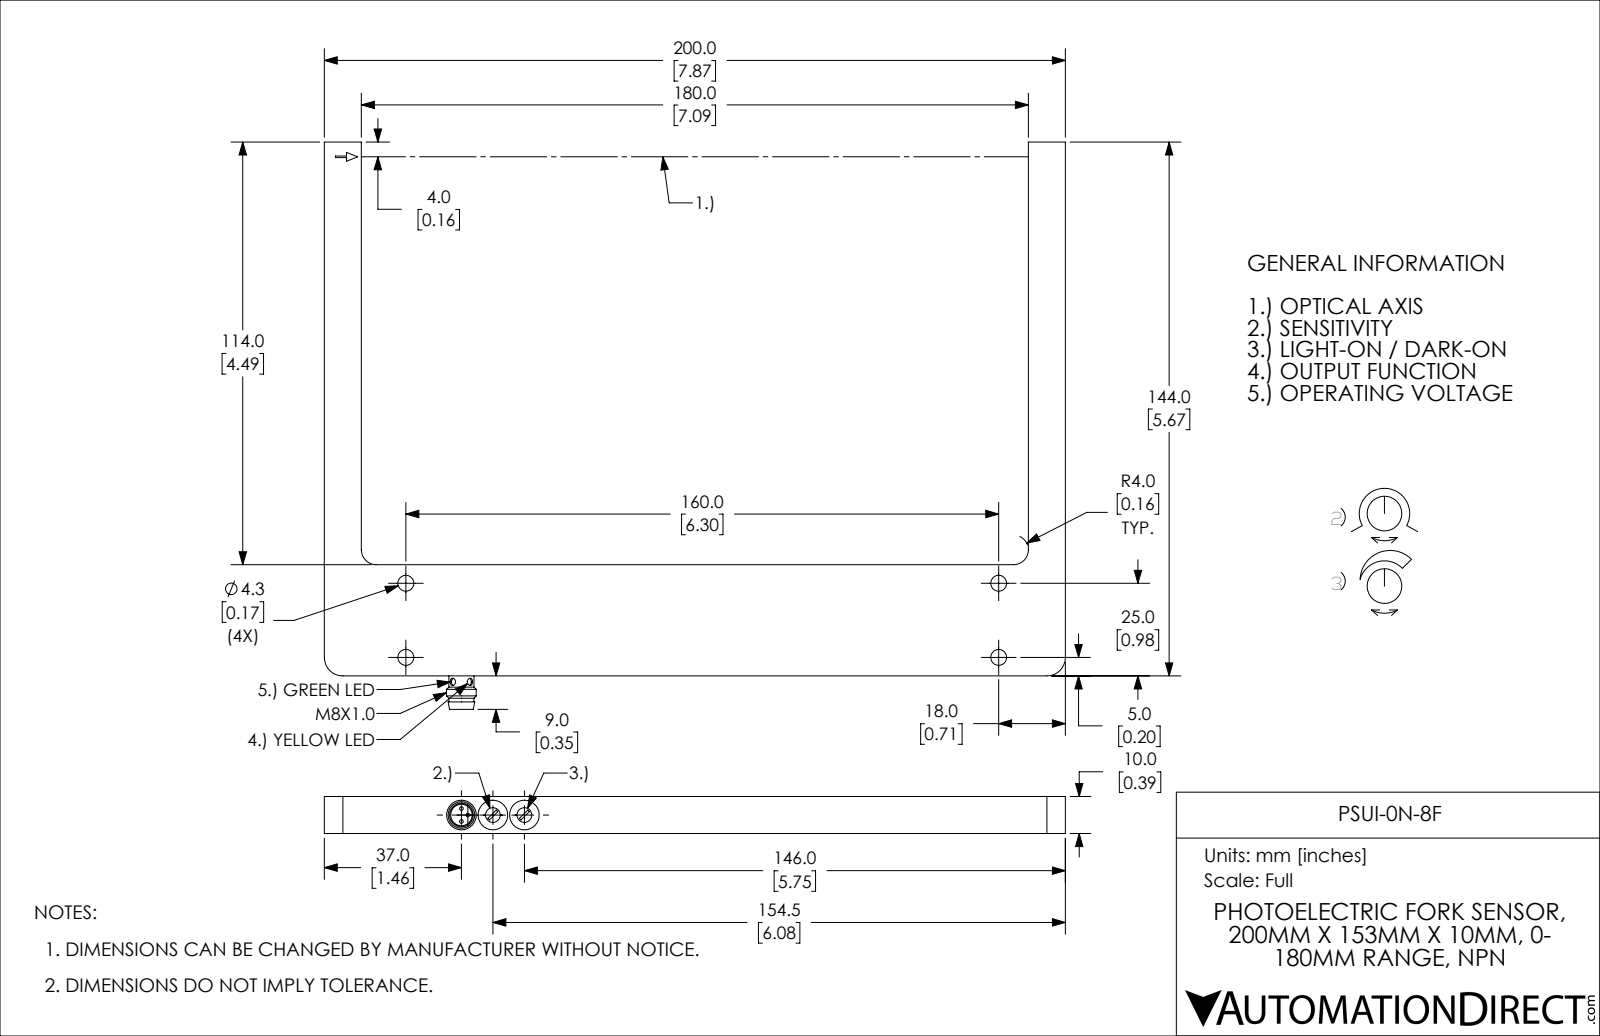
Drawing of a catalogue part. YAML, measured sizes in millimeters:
part_name: "PSUI-0N-8F"
step_written_by: "SolidWorks 2017 (AUTOMOTIVE_DESIGN)"
units: millimeters
bodies: {solids: 1, faces: 68, planar: 35, cylindrical: 27, other: 6}
overall_size: [200, 153, 10]
volume: 82390
surface_area: 26430
round_holes:
  - {diameter: 4.3, count: 4}
  - {diameter: 2, count: 2}
  - {diameter: 4, count: 2}
  - {diameter: 8, count: 2}
  - {diameter: 5.8, count: 1}
round_bosses_or_shafts:
  - {diameter: 1, count: 3}
  - {diameter: 8, count: 1}
  - {diameter: 6.8, count: 1}
partial_cylinders:
  - {radius: 1.6, count: 2}
  - {radius: 4, count: 2}
  - {radius: 5, count: 2}
face_to_face_distances: [10, 190, 30, 200, 180, 114, 144, 143.9, 29.9, 4]
hole_center_spacings: [8.5, 20, 160, 161.2, 17]
